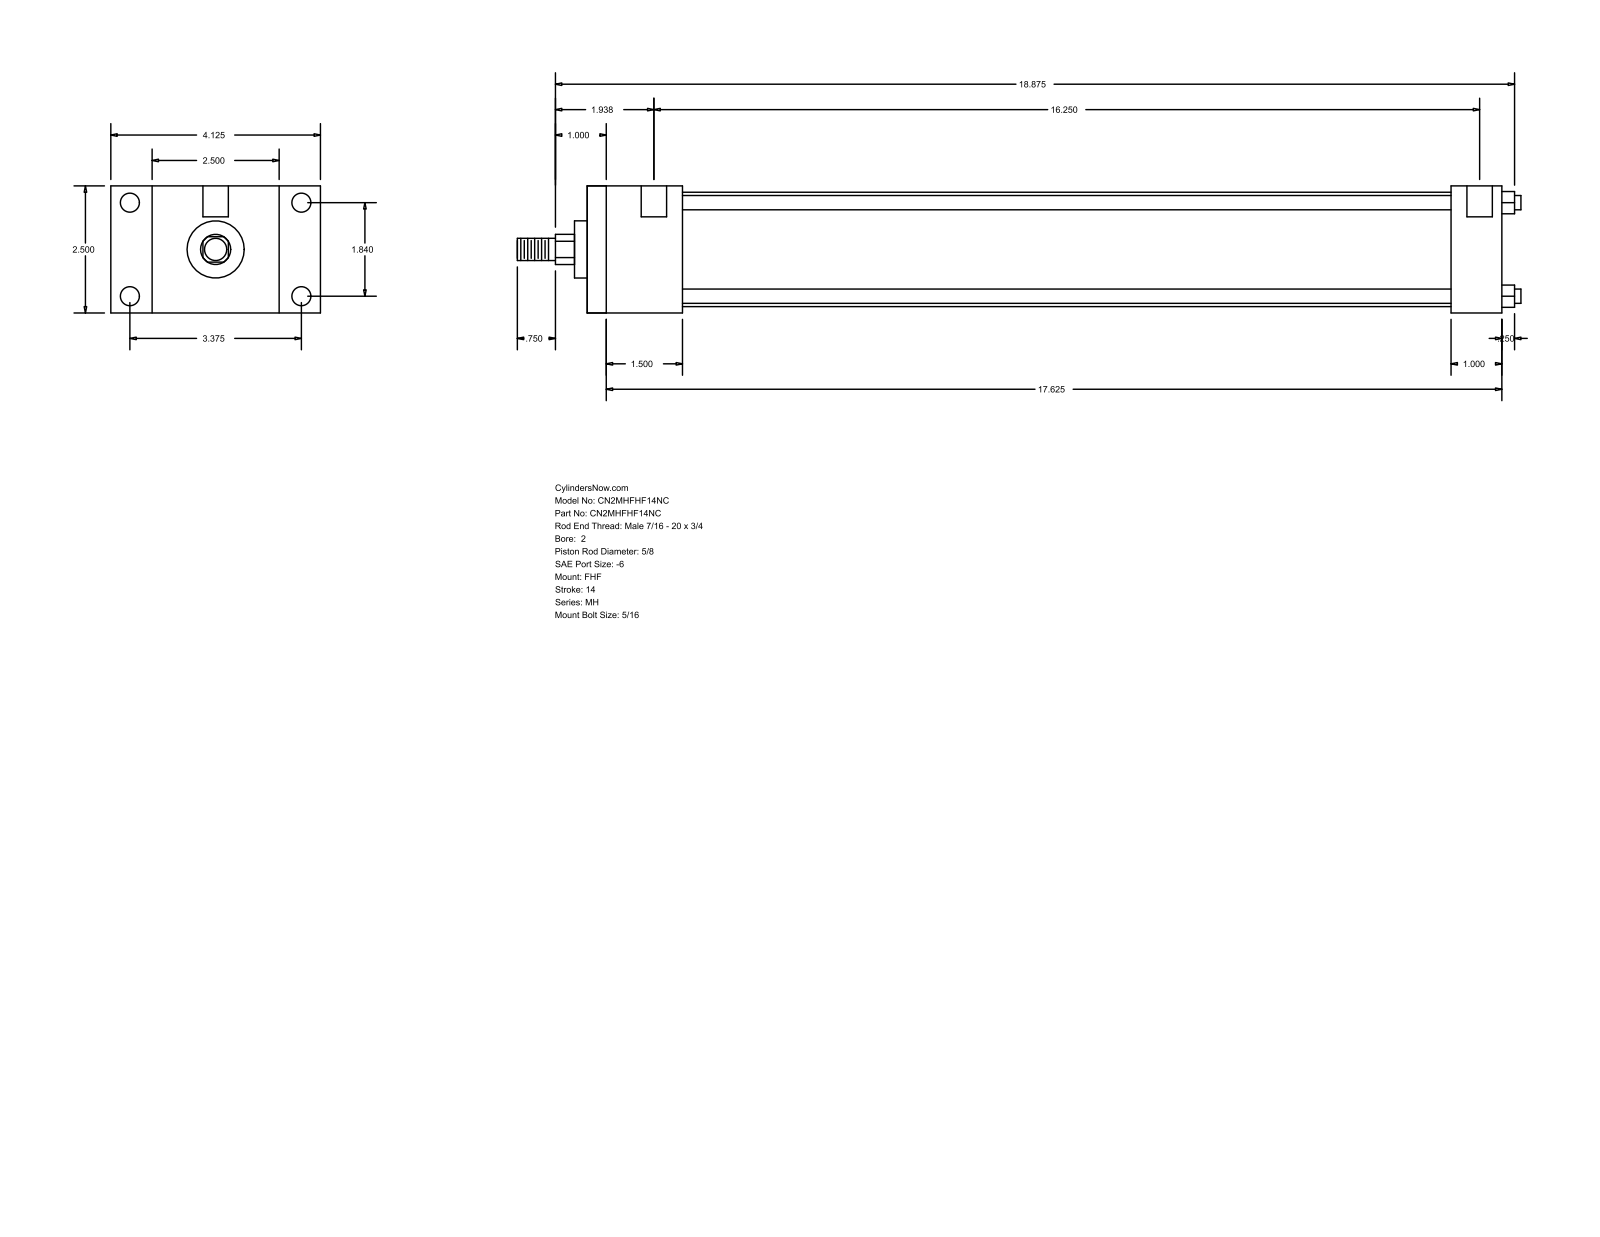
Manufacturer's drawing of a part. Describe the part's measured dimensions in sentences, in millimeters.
The part is named "MH_FHF__0200_0.625". Its 3-D file was written by "GSSL Pune (CONFIG_CONTROL_DESIGN)". It is 0 solids with 88 faces: 60 planar, 28 cylindrical and 0 other. Overall it measures 501.65 by 104.78 by 63.5 millimeters. Round holes: 4 of diameter 5.56, 4 of diameter 9.53, 2 of diameter 12.7. Round bosses or shafts: 4 of diameter 7.14, 1 of diameter 57.15, 1 of diameter 28.57, 1 of diameter 15.88, 1 of diameter 11.11. Partial cylindrical surfaces (rounded edges, fillets, slot ends): 1 of radius 7.54. The main face-to-face distances are 63.5, 47.62, 457.19, 409.57, 20.64, 84.14, 104.78, 431.8, 384.18, 25.39. The hole center spacings are 46.74, 85.72, 97.63, 420.69, 3.18, 4.76, 412.75, 415.93.
